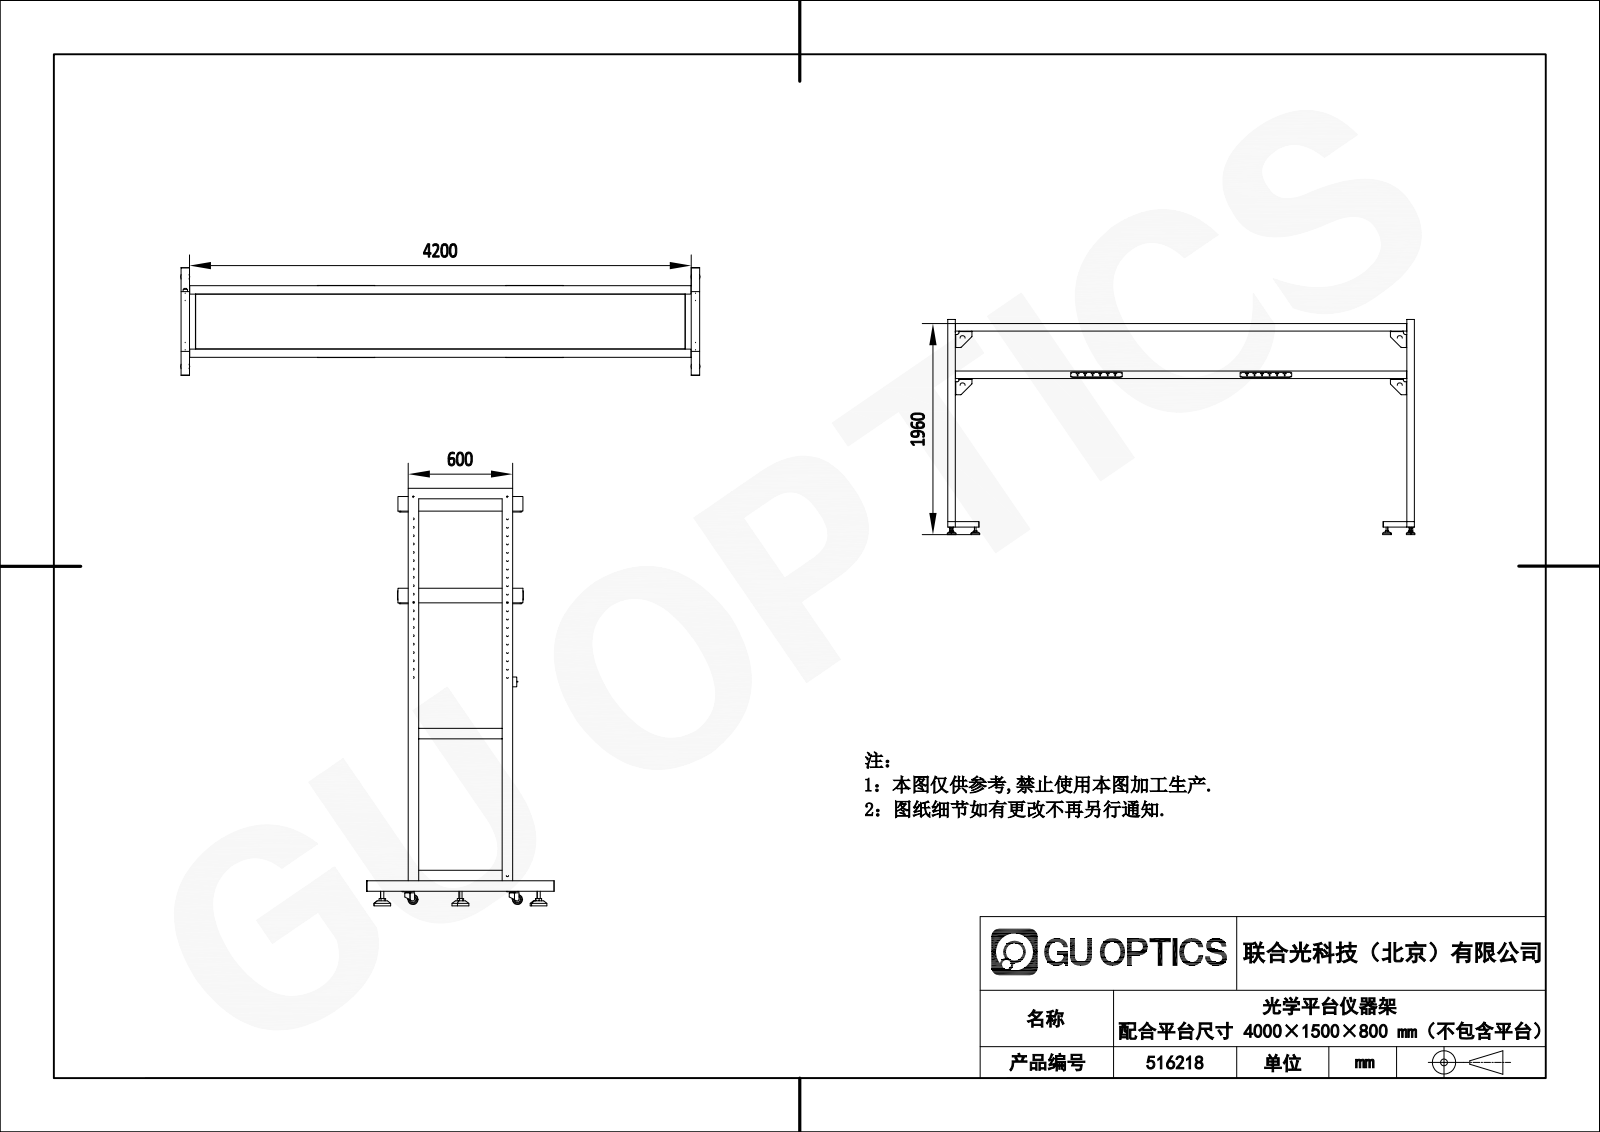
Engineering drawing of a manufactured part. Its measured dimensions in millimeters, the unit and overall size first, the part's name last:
Units: millimetres
Overall size (bounding box): 4350 × 2001 × 900
Round holes (diameter × count): ⌀9 ×66, ⌀6.1 ×16, ⌀10 ×16, ⌀6.5 ×12, ⌀4.2 ×8, ⌀5.2 ×8, ⌀6 ×8, ⌀17 ×6, ⌀18 ×6, ⌀26 ×6, ⌀69 ×6, ⌀3.2 ×4
Round bosses / shafts (diameter × count): ⌀80 ×6, ⌀16 ×6, ⌀26 ×4, ⌀18 ×4, ⌀50 ×2, ⌀10 ×2
Partial cylindrical surfaces — rounded edges, fillets, slot ends (radius × count): R5 ×36, R7 ×24, R3 ×16, R4.25 ×12, R1.5 ×8, R1.51 ×8, R4.01 ×8, R13 ×4
Main face-to-face distances: 440, 1.5, 3, 70, 67, 438.5, 2.5, 67.5, 441.5, 530
Hole centre spacings: 40, 80, 120, 280, 160, 200, 240, 320
Volume: 32 430 000 mm³ · Surface area: 24 370 000 mm²
Bodies: 55 solids, 2593 faces (1445 planar, 1072 cylindrical, 76 other)
Part name (STEP PRODUCT): 516218
STEP written by: SolidWorks 2020 (AUTOMOTIVE_DESIGN)
